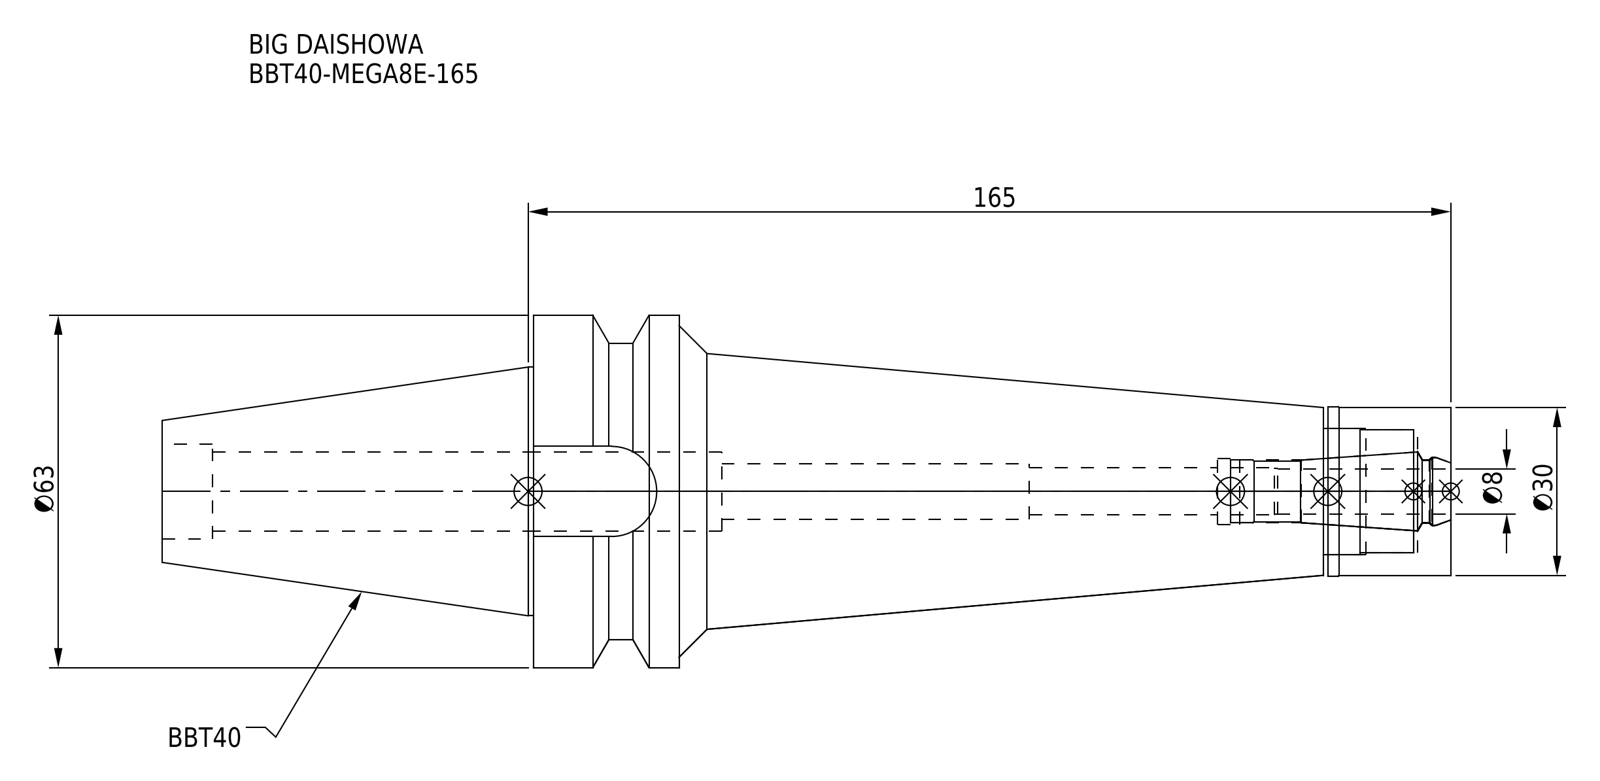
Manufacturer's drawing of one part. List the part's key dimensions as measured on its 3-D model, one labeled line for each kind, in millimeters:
Part name (STEP PRODUCT): BBT40ME08165-080_ASM.stp; BBT40-MEGA8E-165-080-FreeParts; BBT40-MEGA8E-165_1.stp; DXF_TEMP_ASSY_ASM_4_ASM.stp (+3 more)
STEP written by: SolidWorks 2019 (CONFIG_CONTROL_DESIGN)
Units: millimetres
Bodies: 2 solids, 81 faces (21 planar, 40 cylindrical, 20 other)
Overall size (bounding box): 230.4 × 63 × 63
Volume: 274 174 mm³ · Surface area: 45 854 mm²
Round holes (diameter × count): ⌀8.4 ×1, ⌀10 ×1, ⌀11.2 ×1, ⌀11.4 ×1, ⌀11.8 ×1, ⌀12.3 ×1, ⌀14.2 ×1, ⌀17 ×1, ⌀22 ×1, ⌀22.5 ×1
Round bosses / shafts (diameter × count): ⌀63 ×1, ⌀53 ×1, ⌀44.45 ×1, ⌀30.3 ×1, ⌀30 ×1
Partial cylindrical surfaces — rounded edges, fillets, slot ends (radius × count): R8.05 ×1
Main face-to-face distances: 164, 16.1, 138, 26, 115.2, 45, 22, 116, 142, 22.8
